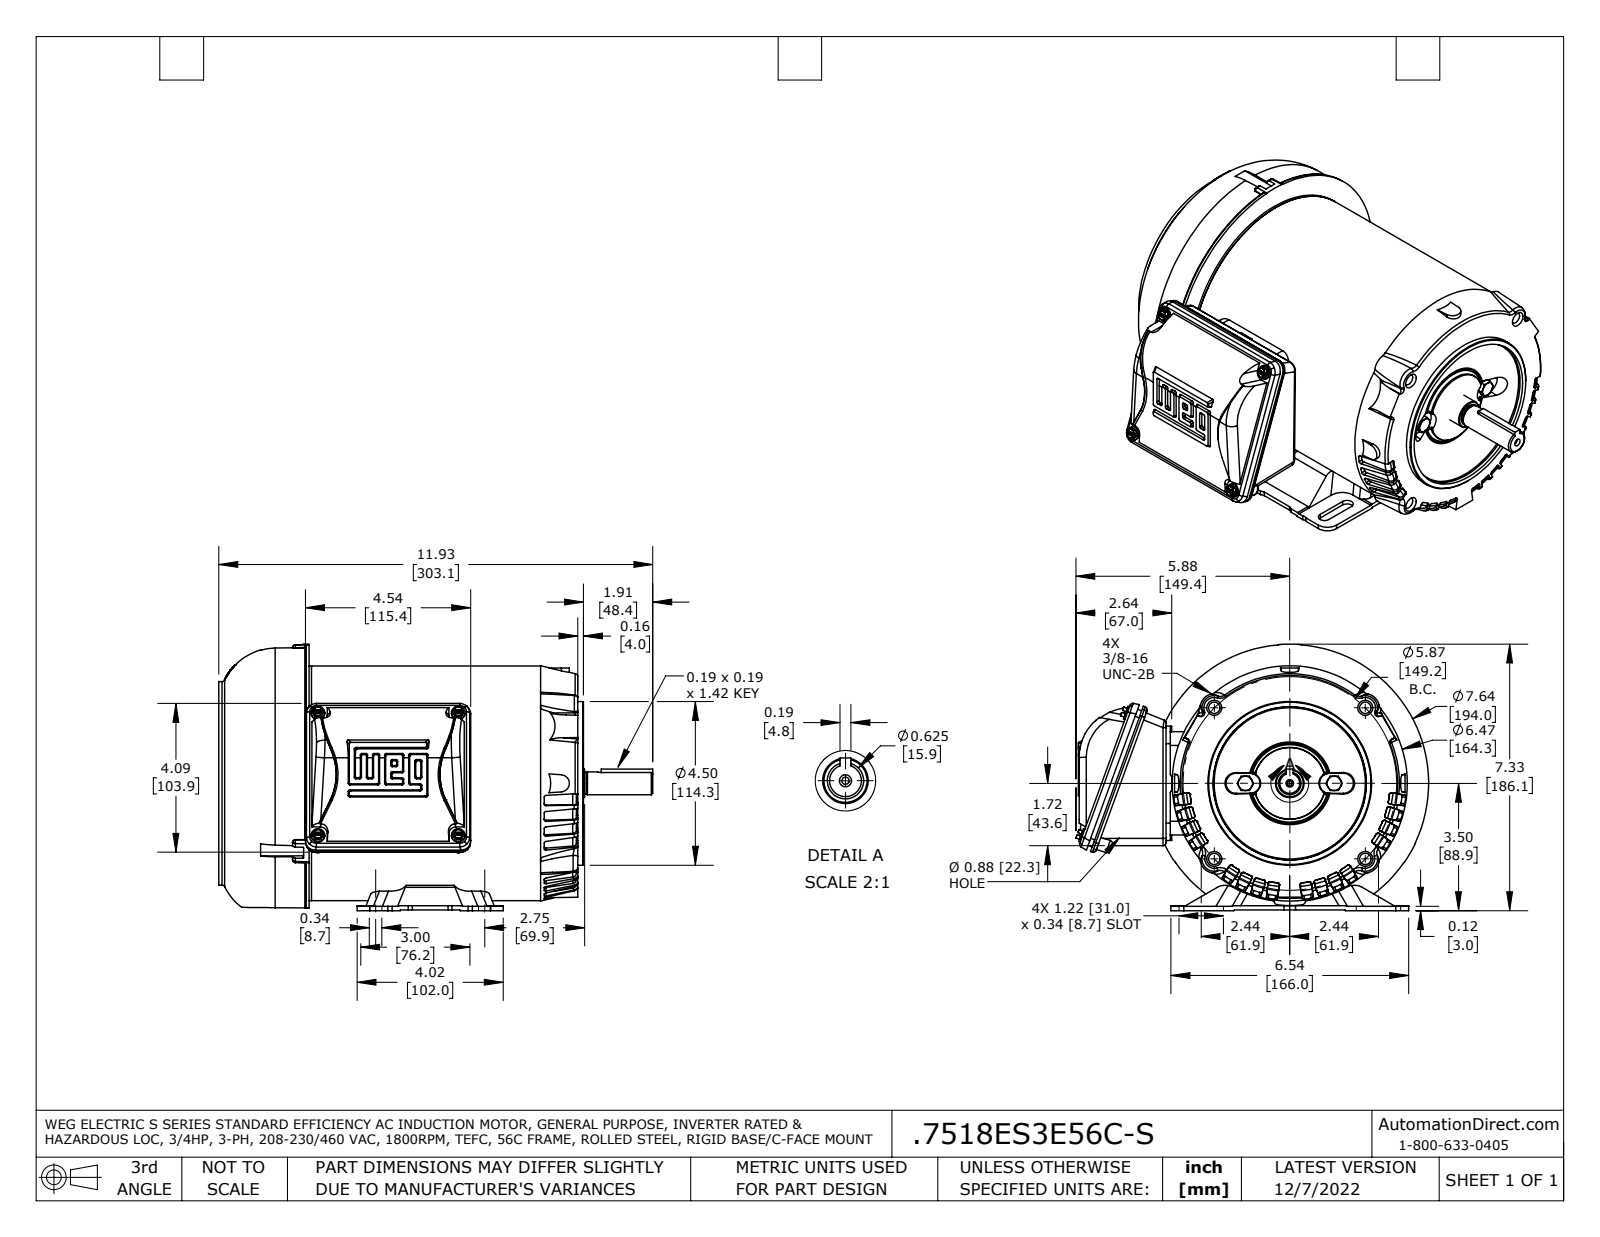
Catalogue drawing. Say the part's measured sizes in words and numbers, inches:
The part is named "56C_3PH_TEFC_GP_11929 fxt". Its 3-D file was written by "SolidWorks 2021 (AUTOMOTIVE_DESIGN)". It is 14 solids with 1417 faces: 539 planar, 331 cylindrical and 547 other. Overall it measures 11.933 by 9.7 by 7.551 inches. Its volume is 371.7 cubic inches and its surface area 657.8 square inches. Round holes: 4 of diameter 0.313, 1 of diameter 0.124. Round bosses or shafts: 4 of diameter 0.374, 2 of diameter 0.35, 1 of diameter 6.447, 1 of diameter 6.447, 1 of diameter 5.591, 1 of diameter 4.5, 1 of diameter 0.783, 1 of diameter 0.625. Partial cylindrical surfaces (rounded edges, fillets, slot ends): 40 of radius 0.047, 38 of radius 0.006, 32 of radius 0.051, 12 of radius 0.059, 12 of radius 0.087, 10 of radius 0.02, 10 of radius 0.079, 8 of radius 0.171. The main face-to-face distances are 6.299, 0.067, 6.366, 2.283, 2.35, 8.65, 9.673, 7.39, 7.323, 1.024. The hole center spacings are 2.937, 4.154, 5.874.
